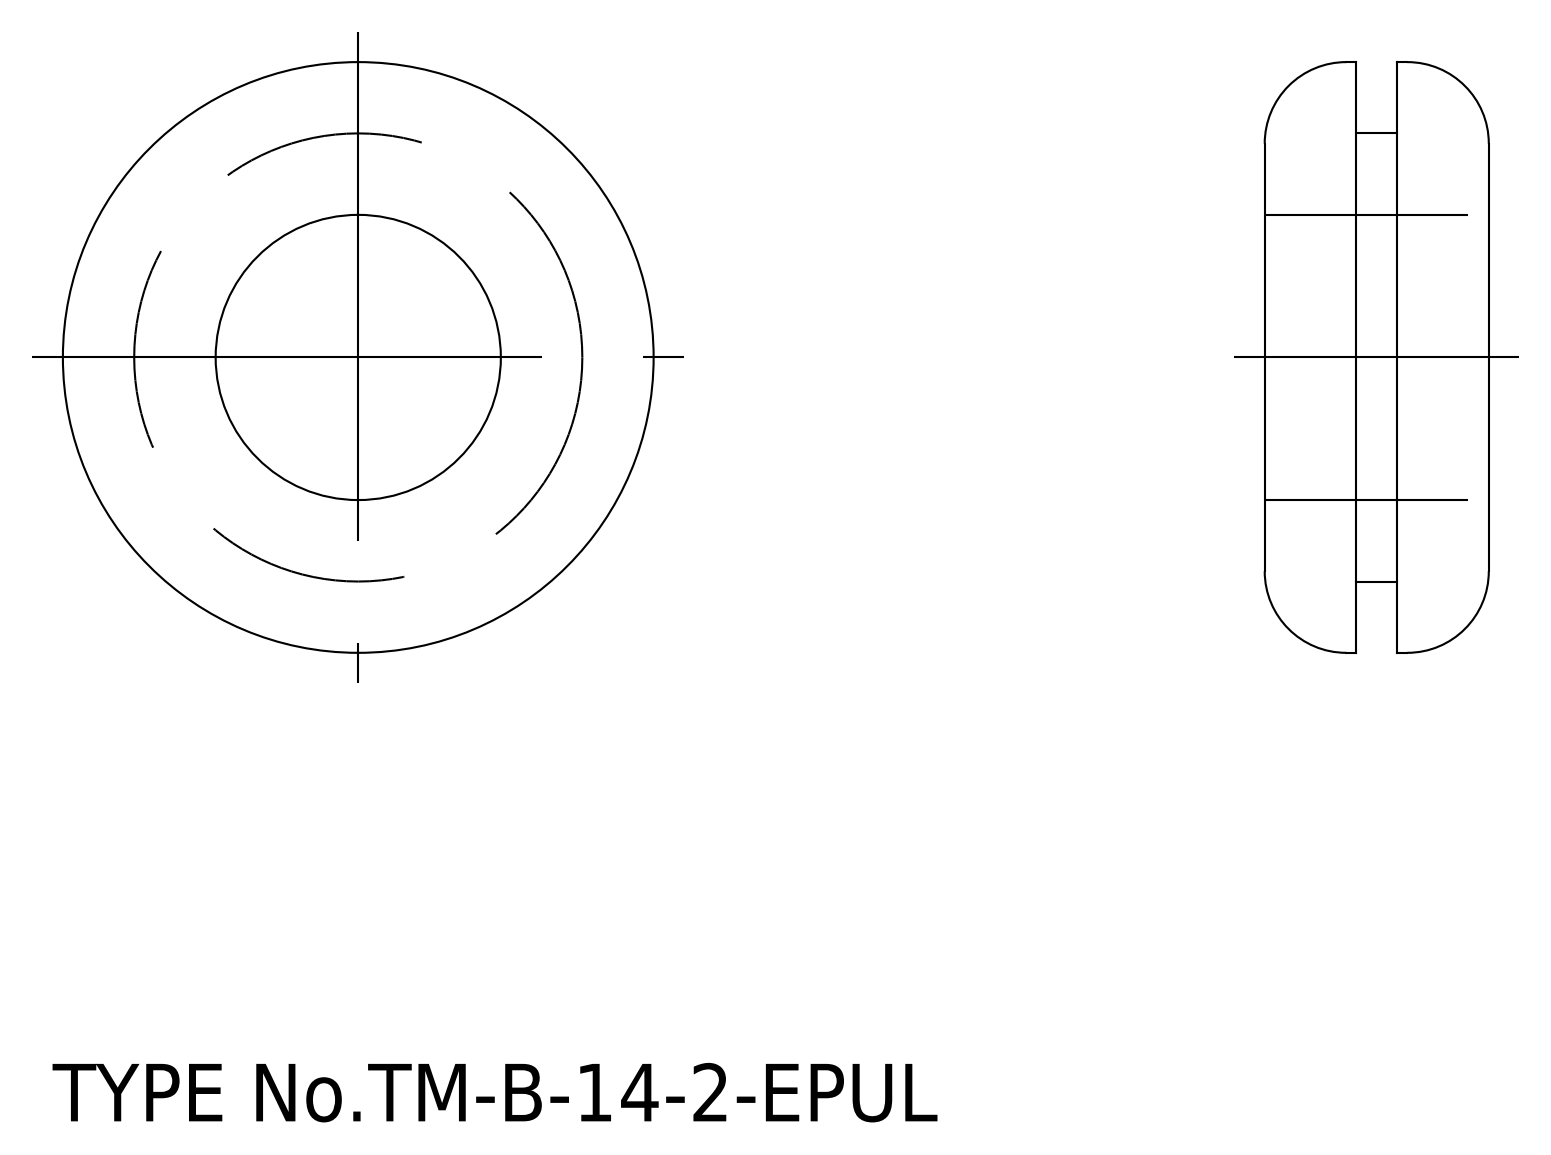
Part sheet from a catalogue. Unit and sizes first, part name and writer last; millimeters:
Units: millimetres
Overall size (bounding box): 29 × 29 × 11
Round holes (diameter × count): ⌀14 ×1
Round bosses / shafts (diameter × count): ⌀29 ×1, ⌀22 ×1
Main face-to-face distances: 4.5, 6.5, 2, 11
Volume: 4 426 mm³ · Surface area: 2 689 mm²
Bodies: 1 solid, 16 faces (4 planar, 8 cylindrical, 4 other)
STEP written by: spGate 15.6.1 (AUTOMOTIVE_DESIGN)
